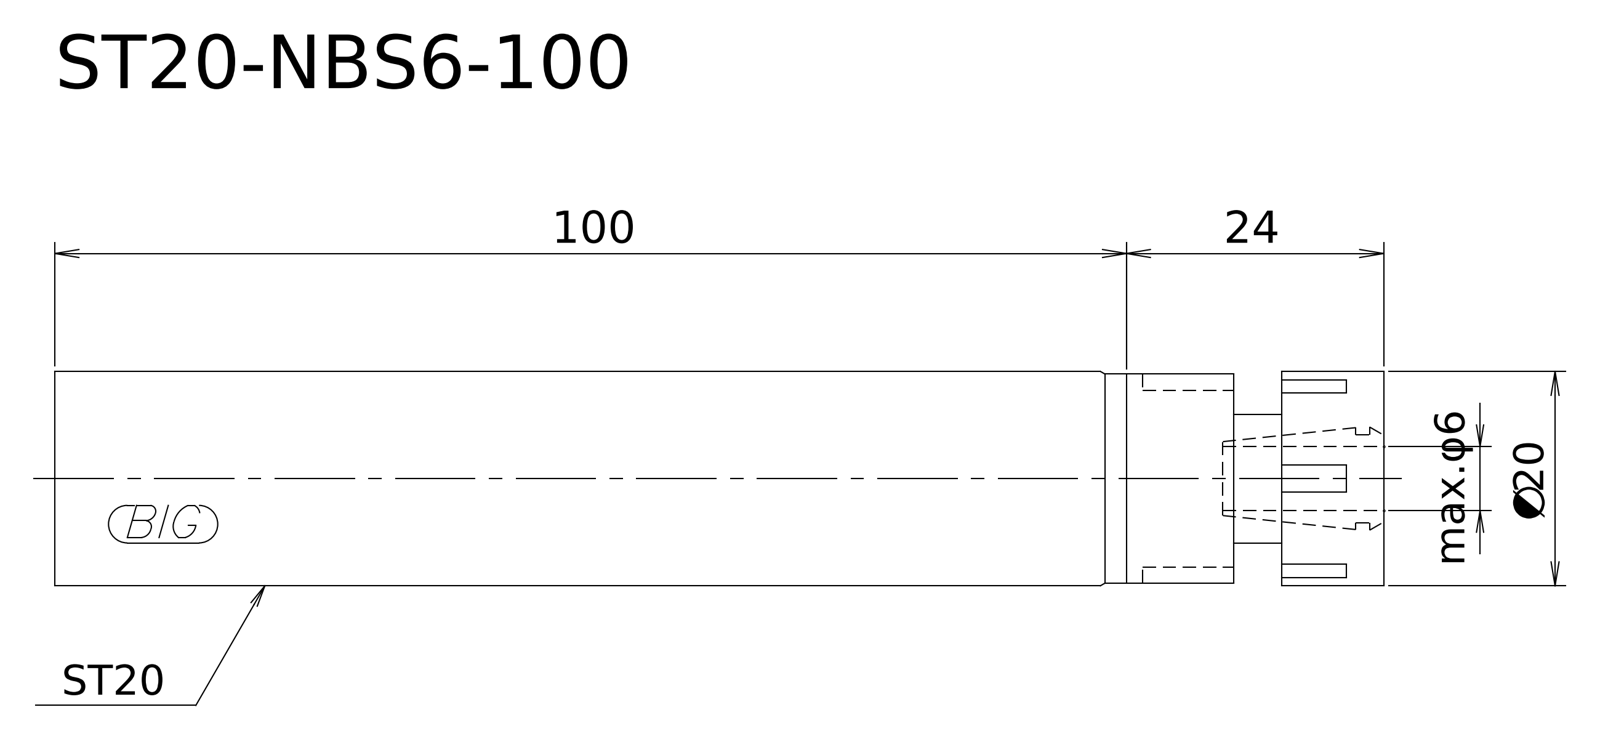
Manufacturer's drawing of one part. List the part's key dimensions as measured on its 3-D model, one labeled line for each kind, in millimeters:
STEP written by: Kubotek KeyCreator V8.5.1 (14335) (CONFIG_CONTROL_DESIGN)
Units: millimetres
Bodies: 1 solid, 9 faces (5 planar, 4 cylindrical, 0 other)
Overall size (bounding box): 124 × 20 × 20
Volume: 37 864 mm³ · Surface area: 8 690 mm²
Round bosses / shafts (diameter × count): ⌀20 ×1, ⌀19.5 ×1, ⌀12 ×1
Main face-to-face distances: 124, 9.5, 114.5, 14, 4.5, 110, 26.05, 16.55, 12.05, 97.95
